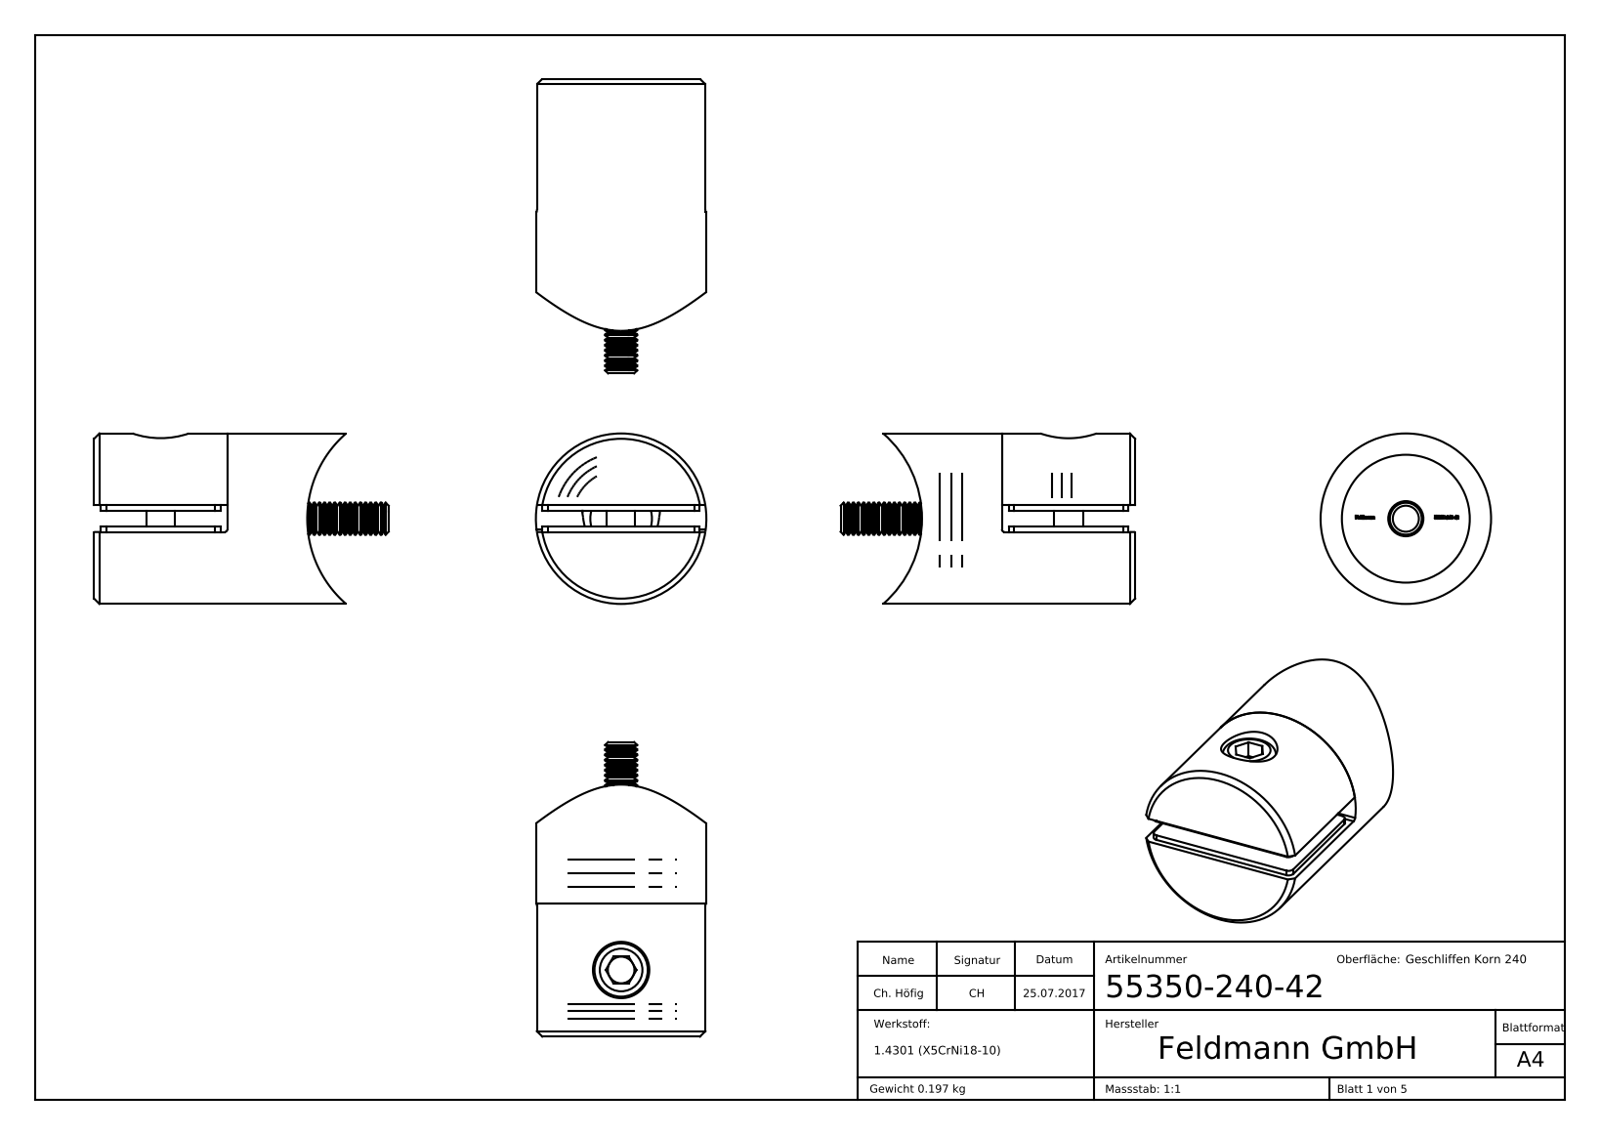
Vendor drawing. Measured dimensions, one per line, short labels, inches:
name: 55350-240-42; 5533X-240 Teil1_55350-240-42 Teil1; socket countersunk head screw_din_DIN 7991 - M6 x 25 --- 25N; 5533x-240 Teil3_55350-240-XX Teil3 (+2 more)
written by: SolidWorks 2018 (CONFIG_CONTROL_DESIGN)
unit: in
bodies: 6 solids, 372 faces (207 planar, 34 cylindrical, 131 other)
size: 2.154 × 1.26 × 1.26
volume: 1.64 in³; area: 21.27 in²
holes: 2× ⌀0.157, 1× ⌀0.197, 1× ⌀0.256, 1× ⌀0.26, 1× ⌀0.276, 1× ⌀0.417, 1× ⌀0.945
bosses: 2× ⌀0.157, 1× ⌀1.26, 1× ⌀0.456, 1× ⌀0.394, 1× ⌀0.236, 1× ⌀0.211
rounds: 4× R0.039, 1× R0.02, 1× R0.281, 1× R0.287, 1× R0.835
face distances: 0.157, 0.039, 0.197, 0.118, 0.984, 0.374, 1.358, 0.295, 0.413, 0.256
hole spacings: 0.376, 0.512
